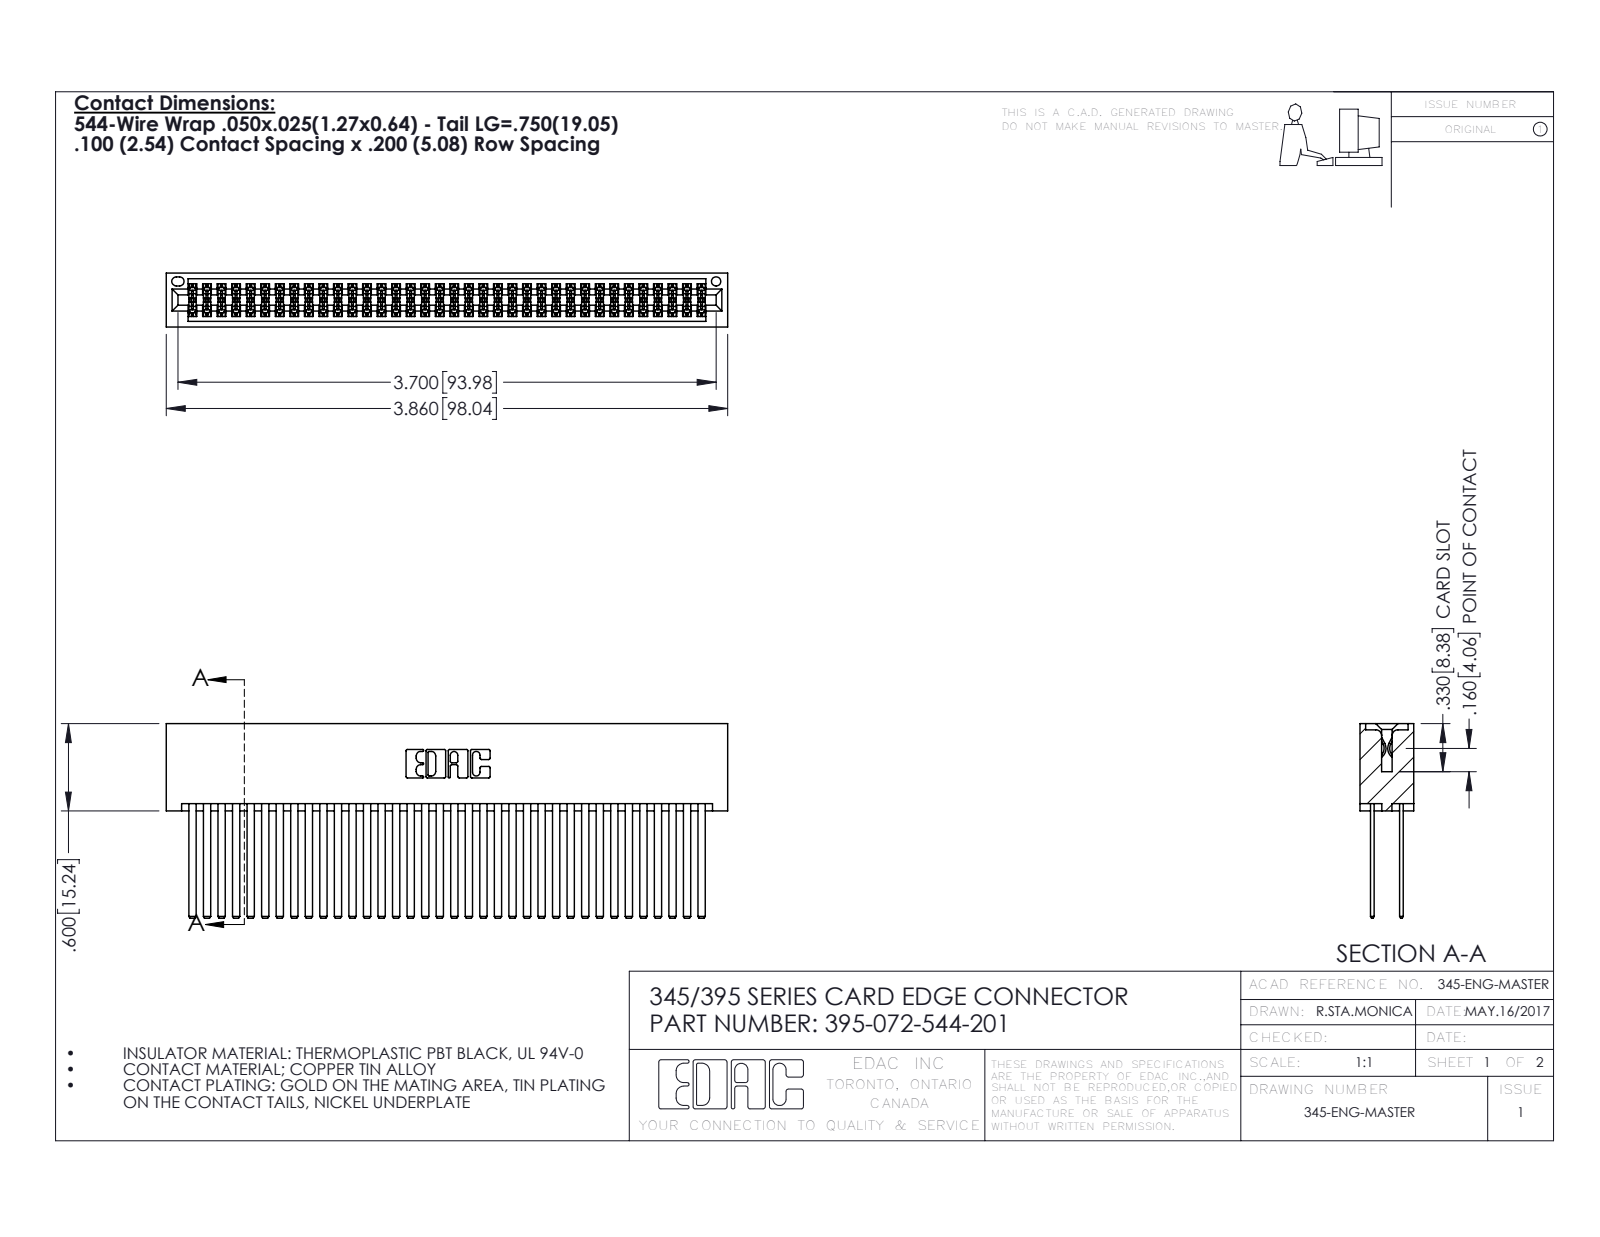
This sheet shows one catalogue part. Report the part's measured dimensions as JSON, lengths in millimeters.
{"part_name": "345-292-001_345-293-144; 395-072-544-201; 345 Part_No Mounting Lugs", "step_written_by": "SolidWorks 2016 (CONFIG_CONTROL_DESIGN)", "units": "millimeters", "bodies": {"solids": 73, "faces": 3286, "planar": 2164, "cylindrical": 1122, "other": 0}, "overall_size": [98, 34, 9.4], "volume_mm3": 11100, "surface_area_mm2": 19540, "round_holes": [[1.6, 1]], "partial_cylinders_radius": [[0.2, 108], [0.3, 22], [0.2, 6], [0.8, 6], [0.7, 3], [0.4, 2], [0.5, 2], [0.6, 2]], "face_to_face_distances": [5.1, 0.6, 7.6, 1.8, 2.5, 6.9, 5.7, 4.4, 9.4, 1.3]}
